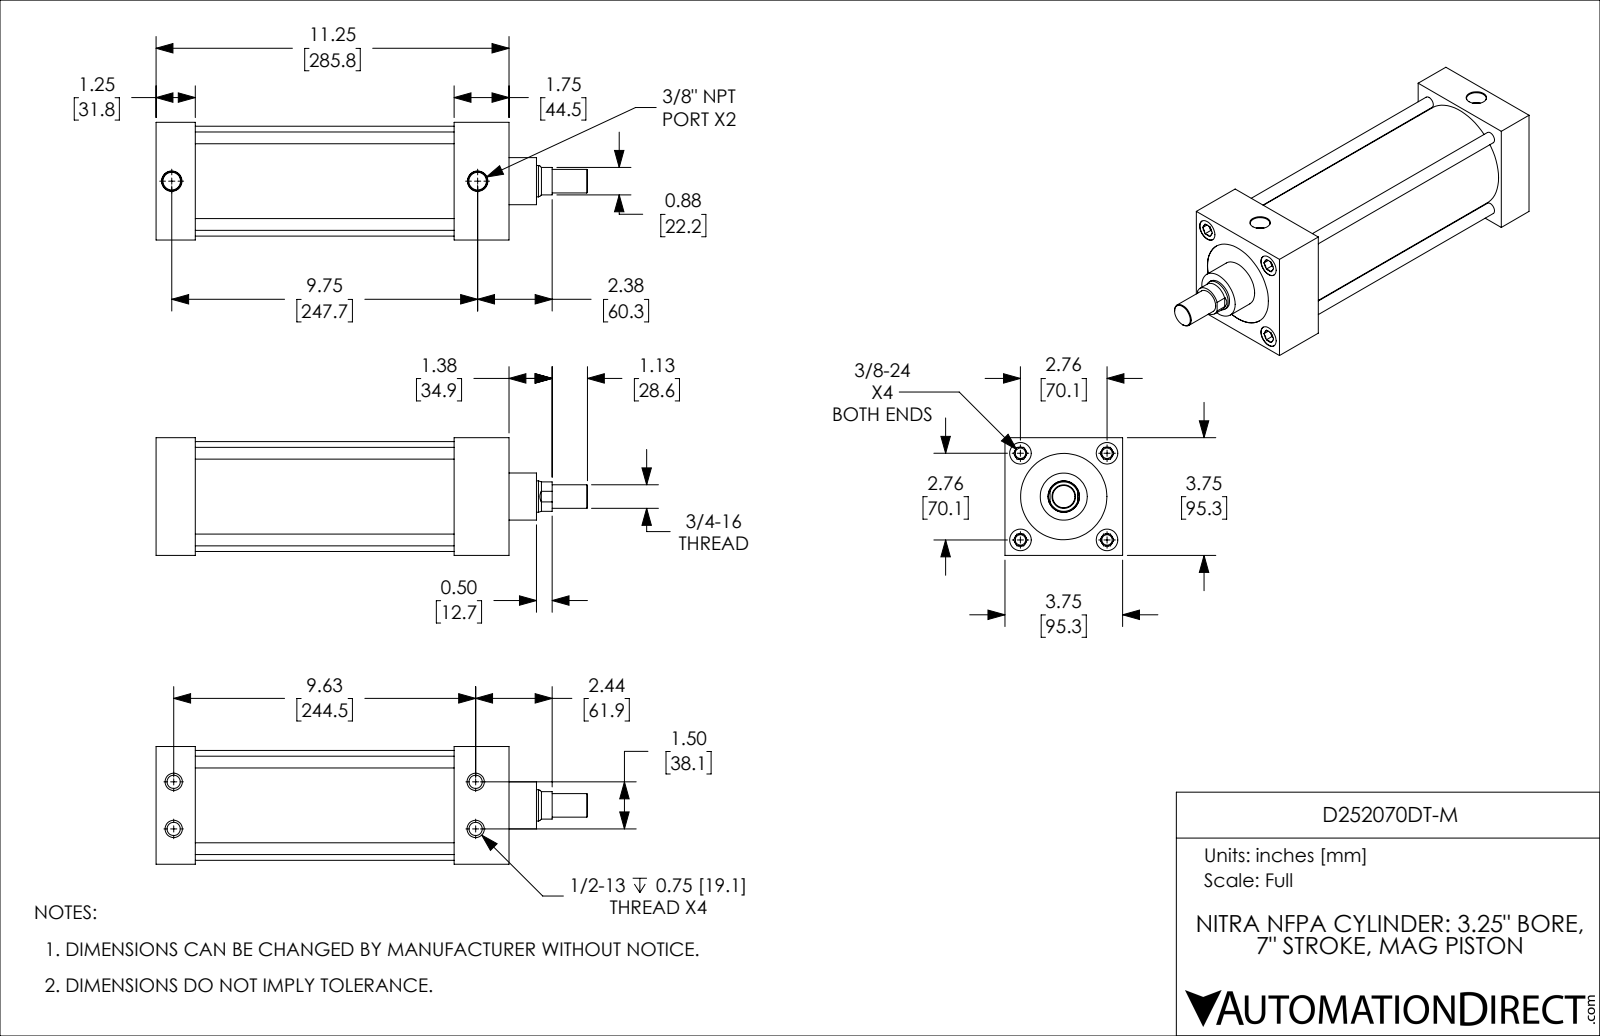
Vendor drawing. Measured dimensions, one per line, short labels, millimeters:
name: D252070DT-M_PISTON_KK1; D252070DT-M_BODY; D252070DT-M
written by: SolidWorks 2019 (CONFIG_CONTROL_DESIGN)
unit: mm
bodies: 2 solids, 198 faces (58 planar, 62 cylindrical, 78 other)
size: 349.3 × 95.3 × 95.3
volume: 1 193 000 mm³; area: 261 200 mm²
holes: 4× ⌀8.4, 4× ⌀10.7, 4× ⌀17.4, 2× ⌀14.3, 1× ⌀25.4, 1× ⌀69.9, 1× ⌀82.6
bosses: 4× ⌀9.5, 1× ⌀88.9, 1× ⌀82.5, 1× ⌀38.1, 1× ⌀25.4, 1× ⌀19.1
rounds: 1× R11.9
face distances: 31.8, 95.3, 241.3, 209.6, 63.5, 177.8, 285.8, 254, 222.3, 44.5
hole spacings: 19.1, 49.6, 70.1, 246.8, 38.1, 99.1, 244.5, 247.4
